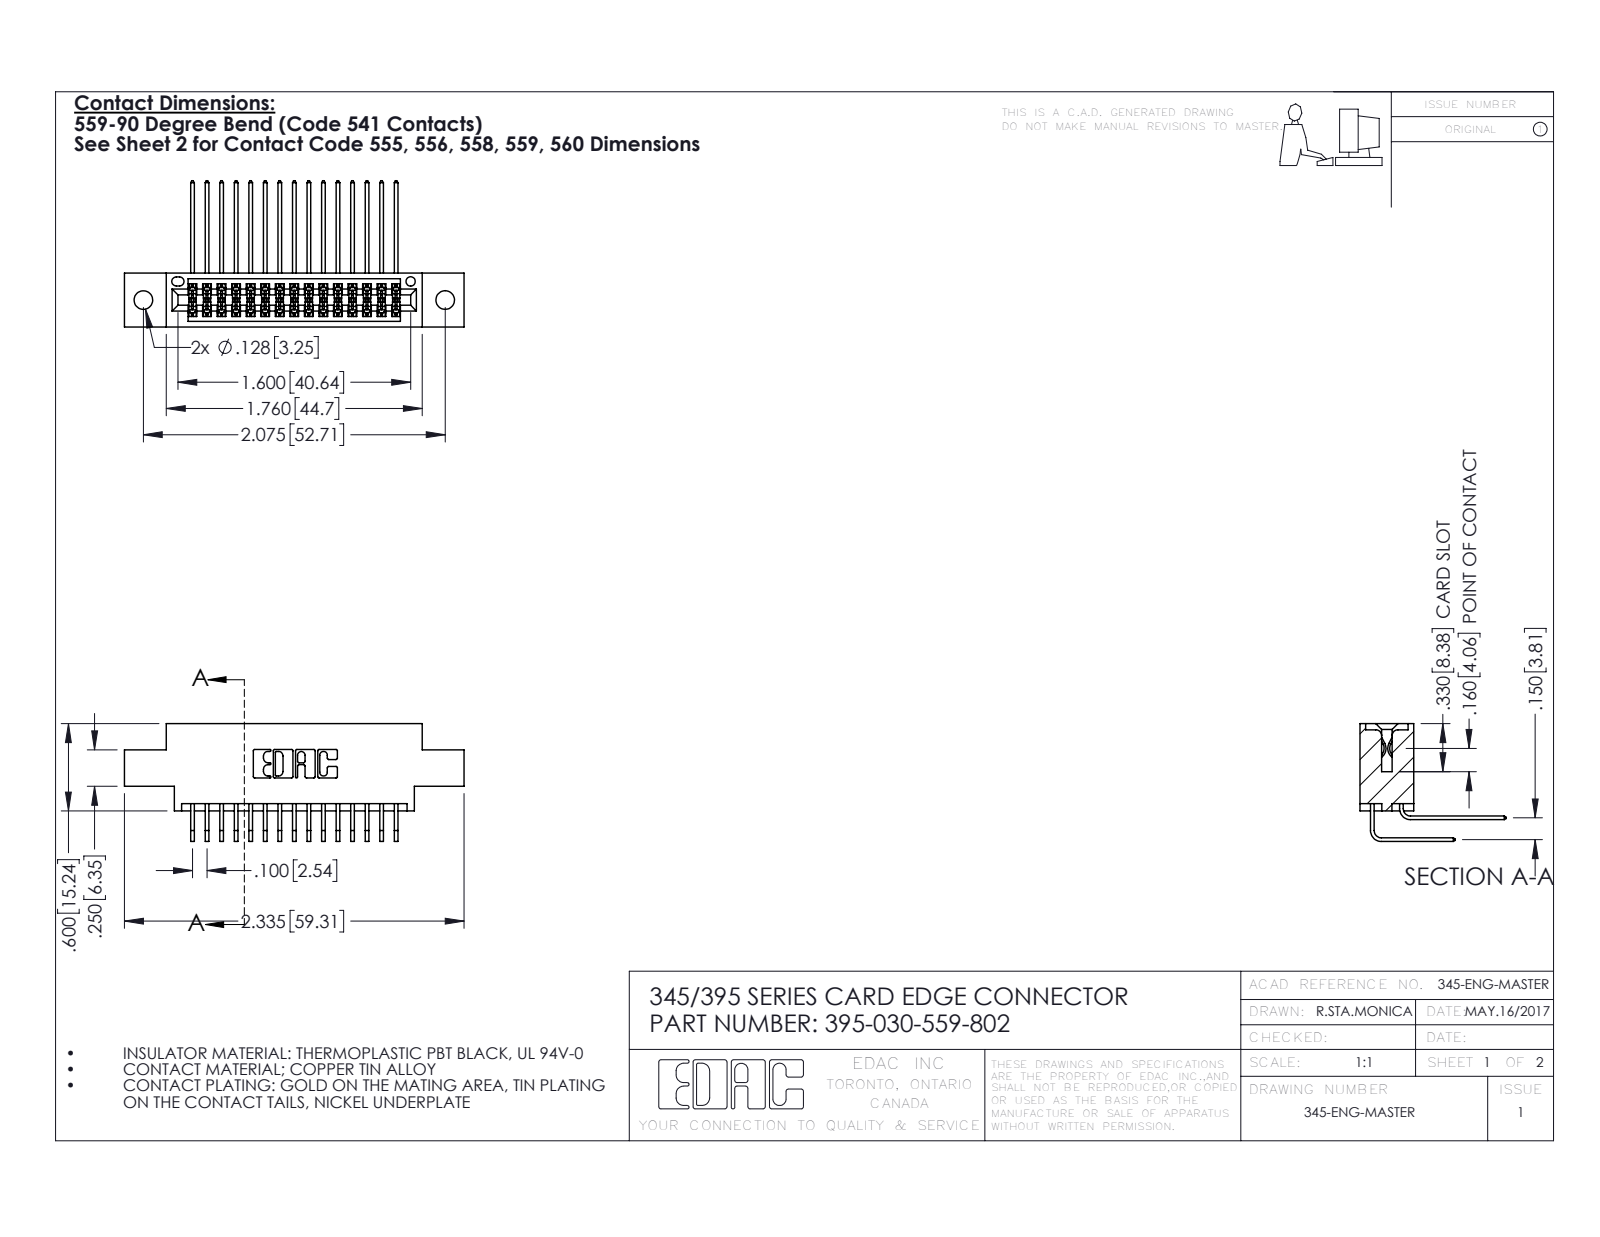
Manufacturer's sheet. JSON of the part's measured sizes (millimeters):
{"part_name": "345 Part_0.170 Offset - 0.128 Dia; 345-292-001_559 Tail - 2; 345-292-001_558 559 Tail - 1; 395-030-559-802", "step_written_by": "SolidWorks 2016 (CONFIG_CONTROL_DESIGN)", "units": "millimeters", "bodies": {"solids": 31, "faces": 1690, "planar": 1134, "cylindrical": 556, "other": 0}, "overall_size": [59.3, 25.5, 20.5], "volume_mm3": 5540, "surface_area_mm2": 8342, "round_holes": [[3.3, 2], [1.6, 1]], "partial_cylinders_radius": [[0.2, 45], [0.3, 22], [0.2, 6], [0.8, 6], [0.7, 3], [0.4, 2], [0.5, 2], [0.6, 2]], "face_to_face_distances": [1.8, 7.6, 9.4, 5.1, 2.5, 6.9, 0.6, 3.8, 5.7, 4.4], "hole_center_spacings": [6.9, 46.8, 52.7]}
